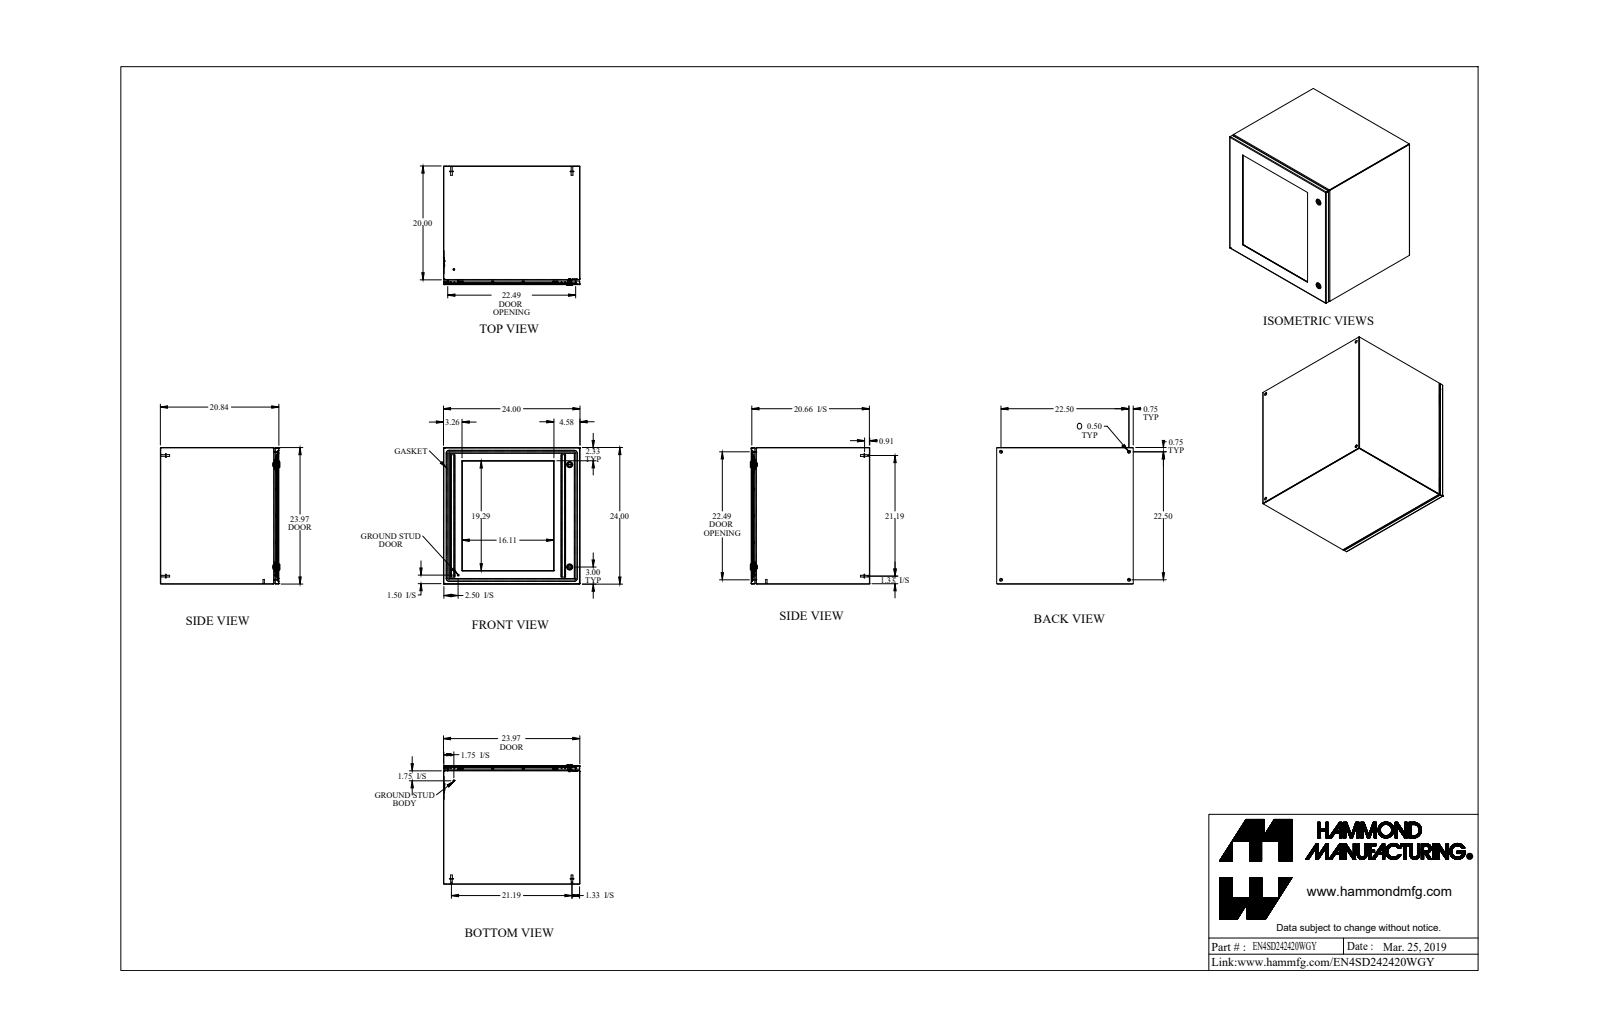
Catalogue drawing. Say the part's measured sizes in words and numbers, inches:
The part is named "EN4SD242420WGY". Its 3-D file was written by "SolidWorks 2019 (AUTOMOTIVE_DESIGN)". It is 74 solids with 1435 faces: 740 planar, 441 cylindrical and 254 other. Overall it measures 24 by 24 by 20.997 inches. Its volume is 313.1 cubic inches and its surface area 7 186 square inches. Round holes: 18 of diameter 0.13, 18 of diameter 0.25, 4 of diameter 0.5, 2 of diameter 0.232, 2 of diameter 0.625, 2 of diameter 0.785, 1 of diameter 0.172, 1 of diameter 0.24, 1 of diameter 0.242. Round bosses or shafts: 19 of diameter 0.226, 18 of diameter 0.368, 18 of diameter 0.164, 4 of diameter 0.625, 4 of diameter 0.313, 4 of diameter 0.27, 2 of diameter 1.1, 2 of diameter 0.525. Partial cylindrical surfaces (rounded edges, fillets, slot ends): 14 of radius 0.036, 14 of radius 0.108, 12 of radius 0.043, 12 of radius 0.081, 12 of radius 0.125, 12 of radius 0.312, 8 of radius 0.1, 4 of radius 0.006. The main face-to-face distances are 0.072, 23.928, 23.856, 24, 20.765, 20.693, 20.443, 0.25, 20.515, 0.322. The hole center spacings are 5.372, 17.781, 4.719, 19.57, 21.03, 5.372, 9.437, 10.743.
